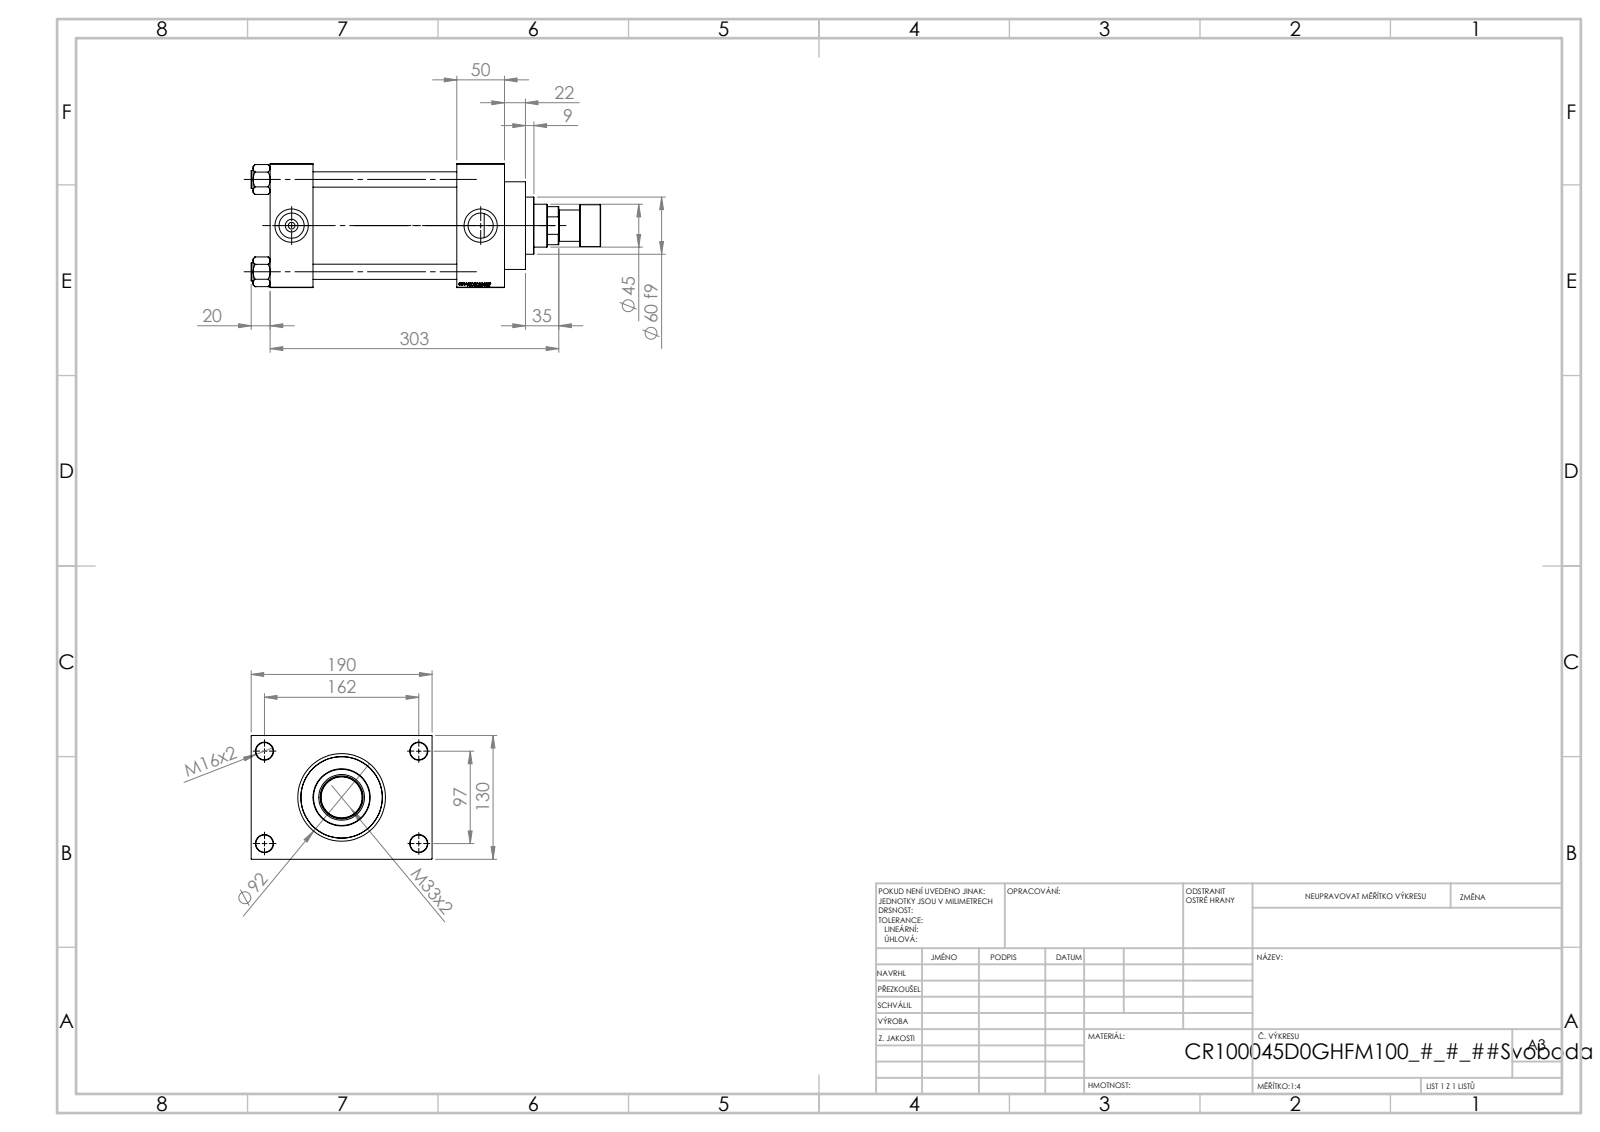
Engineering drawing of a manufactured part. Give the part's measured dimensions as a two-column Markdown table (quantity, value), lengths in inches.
| quantity | value |
| --- | --- |
| part name | V215CR_ROD_END_F; V215CR_D_TYCINKA; NUT_M5_D; V215CR_D_Body (+2 more) |
| STEP written by | SolidWorks 2019 (CONFIG_CONTROL_DESIGN) |
| units | inches |
| bodies | 12 solids, 1164 faces (548 planar, 92 cylindrical, 524 other) |
| overall size | 14.449 × 7.48 × 5.118 |
| volume | 177.7 in³ |
| surface area | 685.8 in² |
| round holes (diameter × count) | 0.63 × 4, 0.709 × 4, 0.276 × 2, 1.041 × 2, 1.378 × 2, 1.24 × 1, 1.772 × 1, 1.89 × 1, 2.992 × 1, 3.366 × 1, 3.937 × 1 |
| round bosses / shafts (diameter × count) | 0.748 × 4, 4.173 × 1, 3.622 × 1, 2.362 × 1, 1.732 × 1, 1.299 × 1 |
| main face-to-face distances | 5.118, 5.945, 1.772, 7.717, 9.685, 7.913, 1.969, 1.181, 6.299, 3.78 |
| hole center spacings | 1.281, 2.698, 3.717, 3.815, 4.026, 5.096, 6.367, 3.819 |
